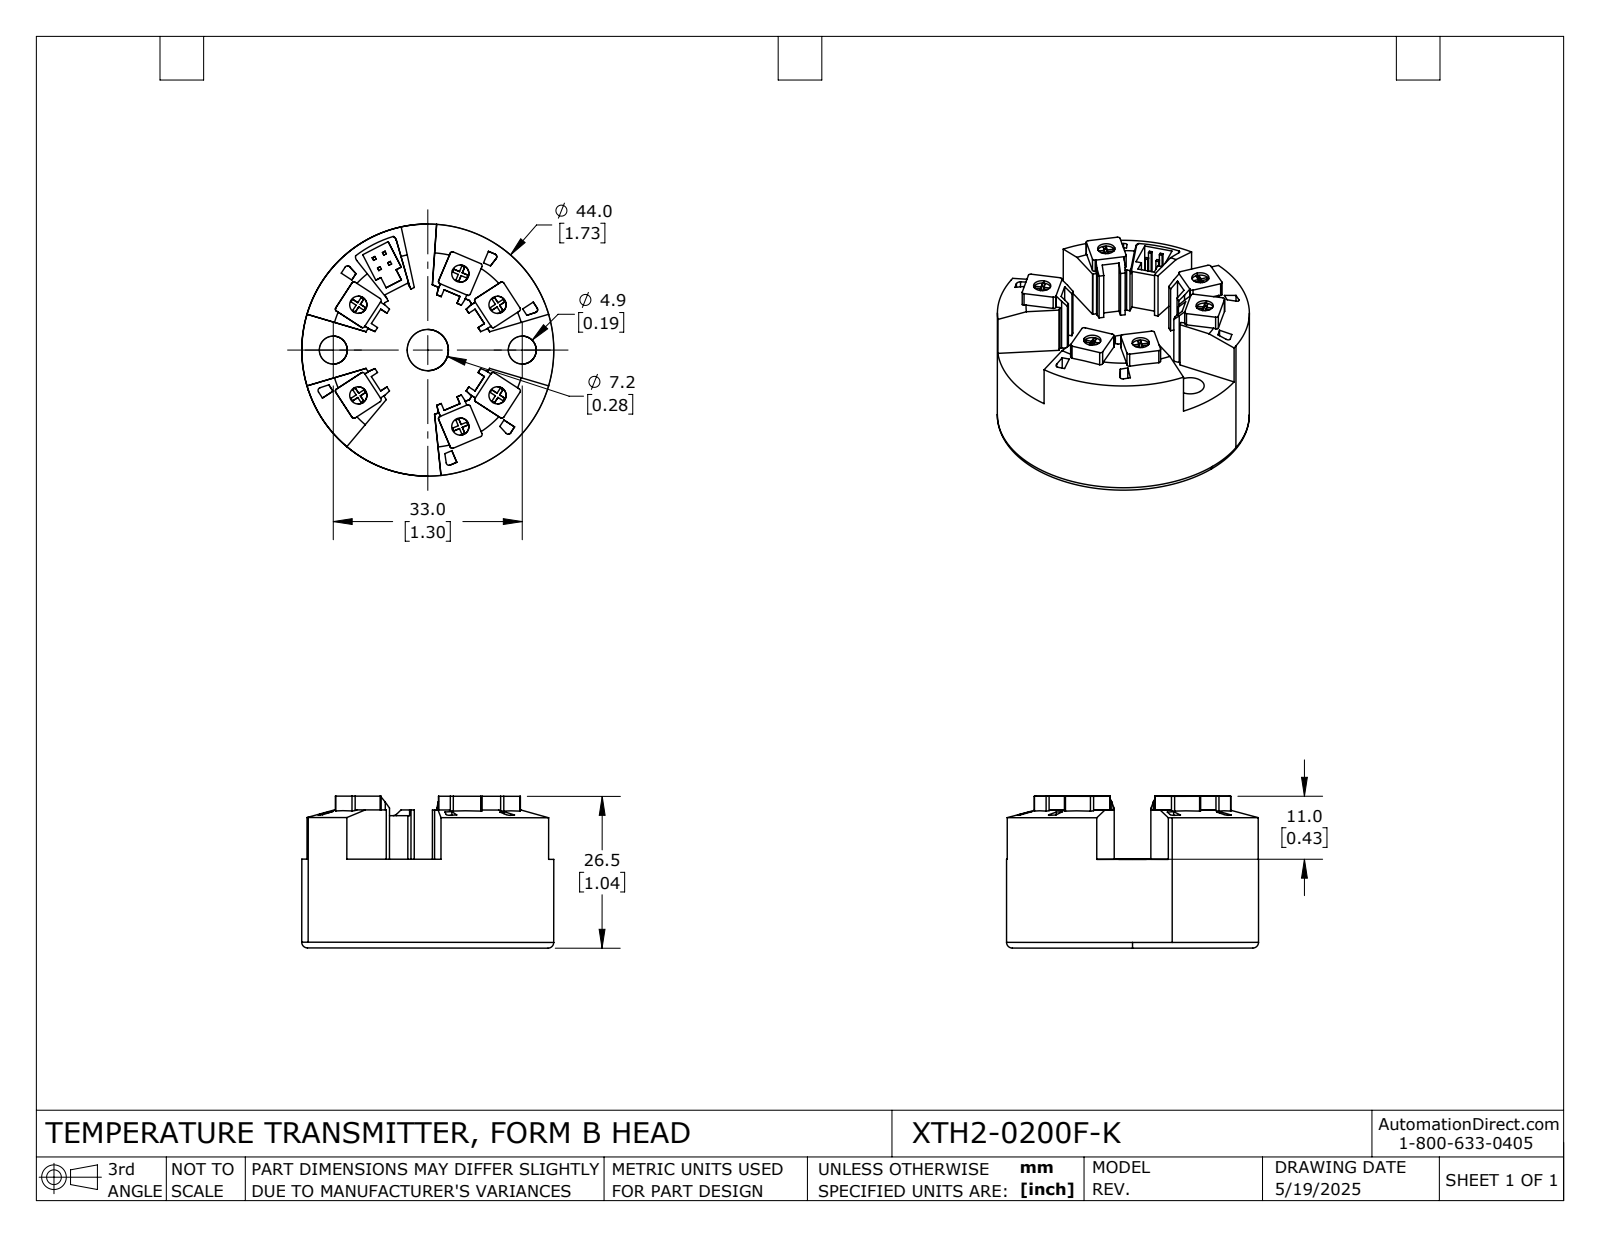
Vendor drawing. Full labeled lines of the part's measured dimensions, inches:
Part name (STEP PRODUCT): XTDH2-0200F-K
STEP written by: SolidWorks 2024 (AUTOMOTIVE_DESIGN)
Units: inches
Bodies: 1 solid, 341 faces (281 planar, 52 cylindrical, 8 other)
Overall size (bounding box): 1.733 × 1.732 × 1.045
Volume: 1.748 in³ · Surface area: 13.46 in²
Round holes (diameter × count): ⌀0.118 ×6, ⌀0.193 ×2, ⌀0.283 ×1
Round bosses / shafts (diameter × count): ⌀1.732 ×1
Partial cylindrical surfaces — rounded edges, fillets, slot ends (radius × count): R0.016 ×24, R0.02 ×6, R0.039 ×2
Main face-to-face distances: 0.61, 1.043, 0.433, 0.059, 0.177, 0.039, 0.02, 0.118, 0.949, 0.339
Hole centre spacings: 0.571, 0.333, 0.355, 0.356, 0.65, 0.677, 0.733, 0.875
